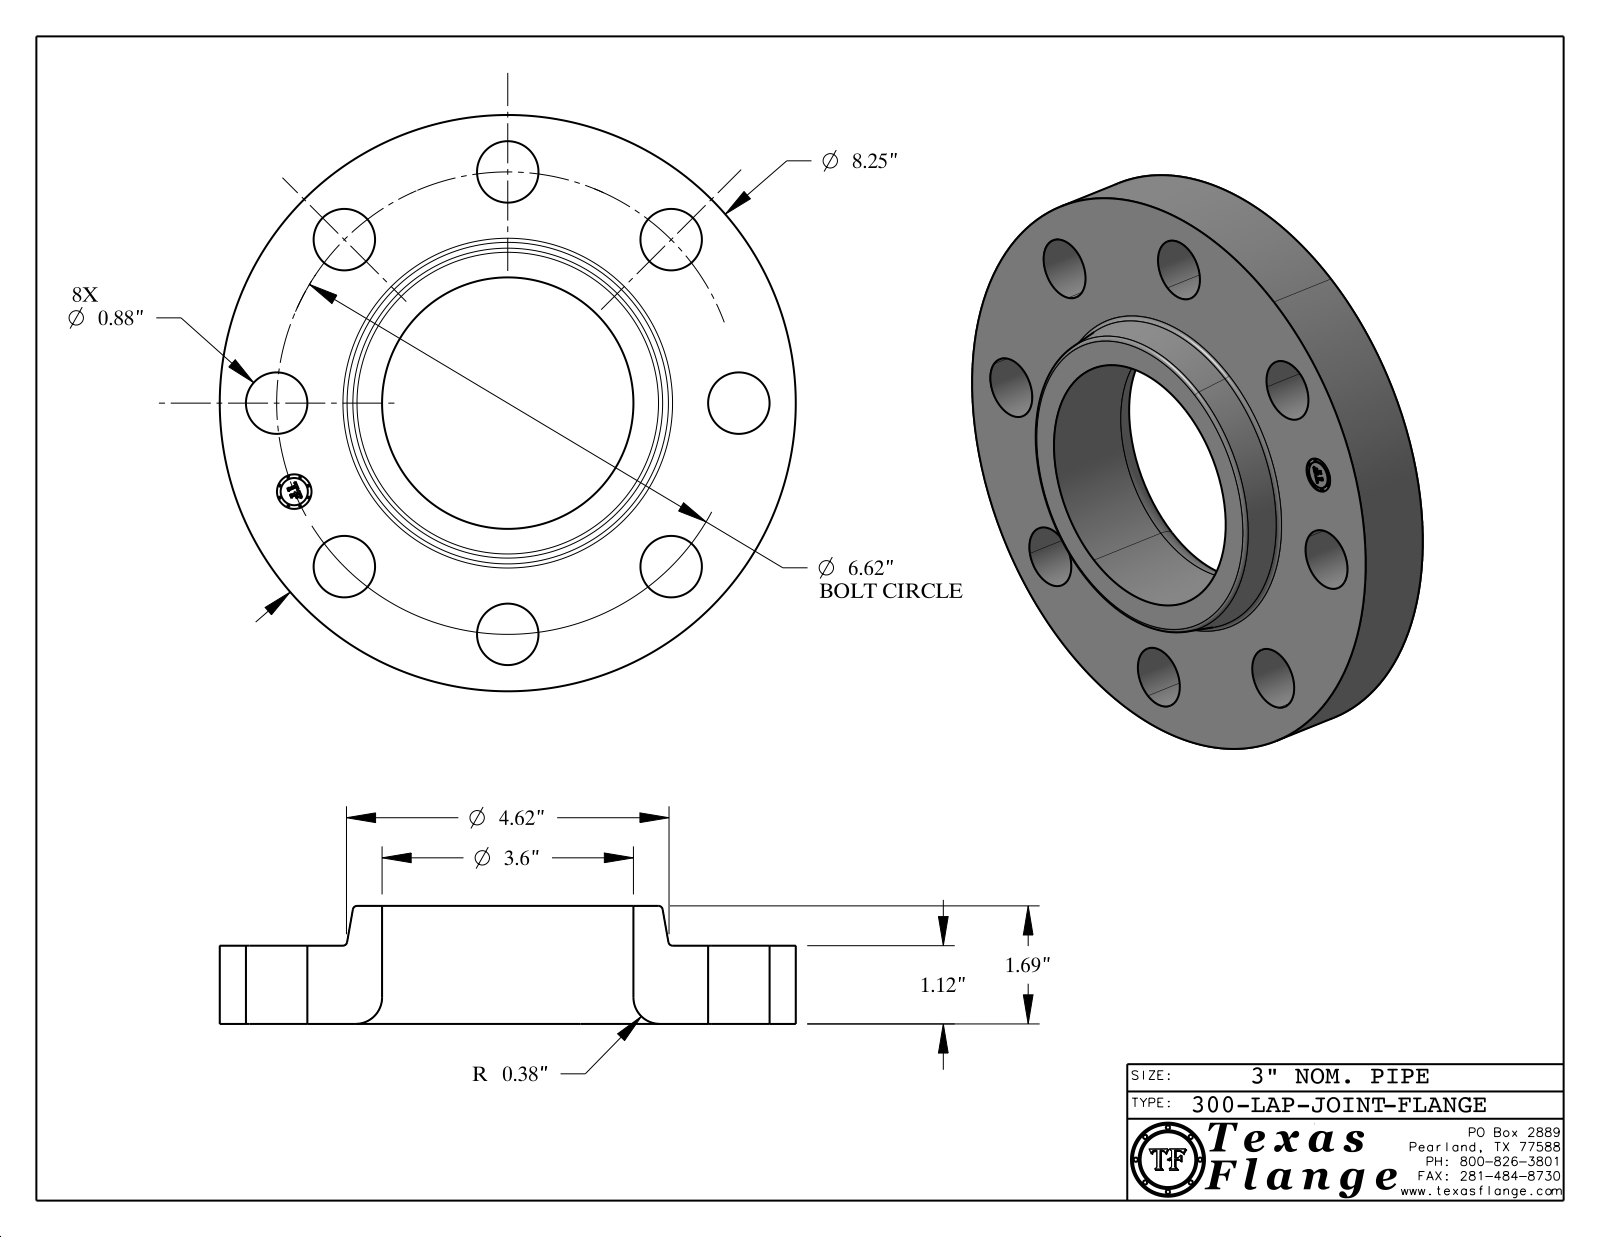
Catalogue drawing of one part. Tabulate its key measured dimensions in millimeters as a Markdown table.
| quantity | value |
| --- | --- |
| part name | 300-LAP-JOINT FLANGE |
| STEP written by | CATIA V5 STEP AP214 (AUTOMOTIVE_DESIGN) |
| units | millimeters |
| bodies | 1 solid, 416 faces (368 planar, 40 cylindrical, 8 other) |
| overall size | 209.6 × 209.6 × 42.9 |
| volume | 753 800 mm³ |
| surface area | 99 610 mm² |
| round holes (diameter × count) | 22.4 × 8, 12.6 × 1, 91.4 × 1 |
| round bosses / shafts (diameter × count) | 0.8 × 8, 209.6 × 1, 9.9 × 1 |
| main face-to-face distances | 28.4, 42.9, 14.5, 0.4, 28.1, 14.9, 3.8, 3.7, 0.7, 2.4 |
| hole center spacings | 84.1, 64.3, 155.3, 118.9, 118.9, 32.8, 93.4, 164.9 |
